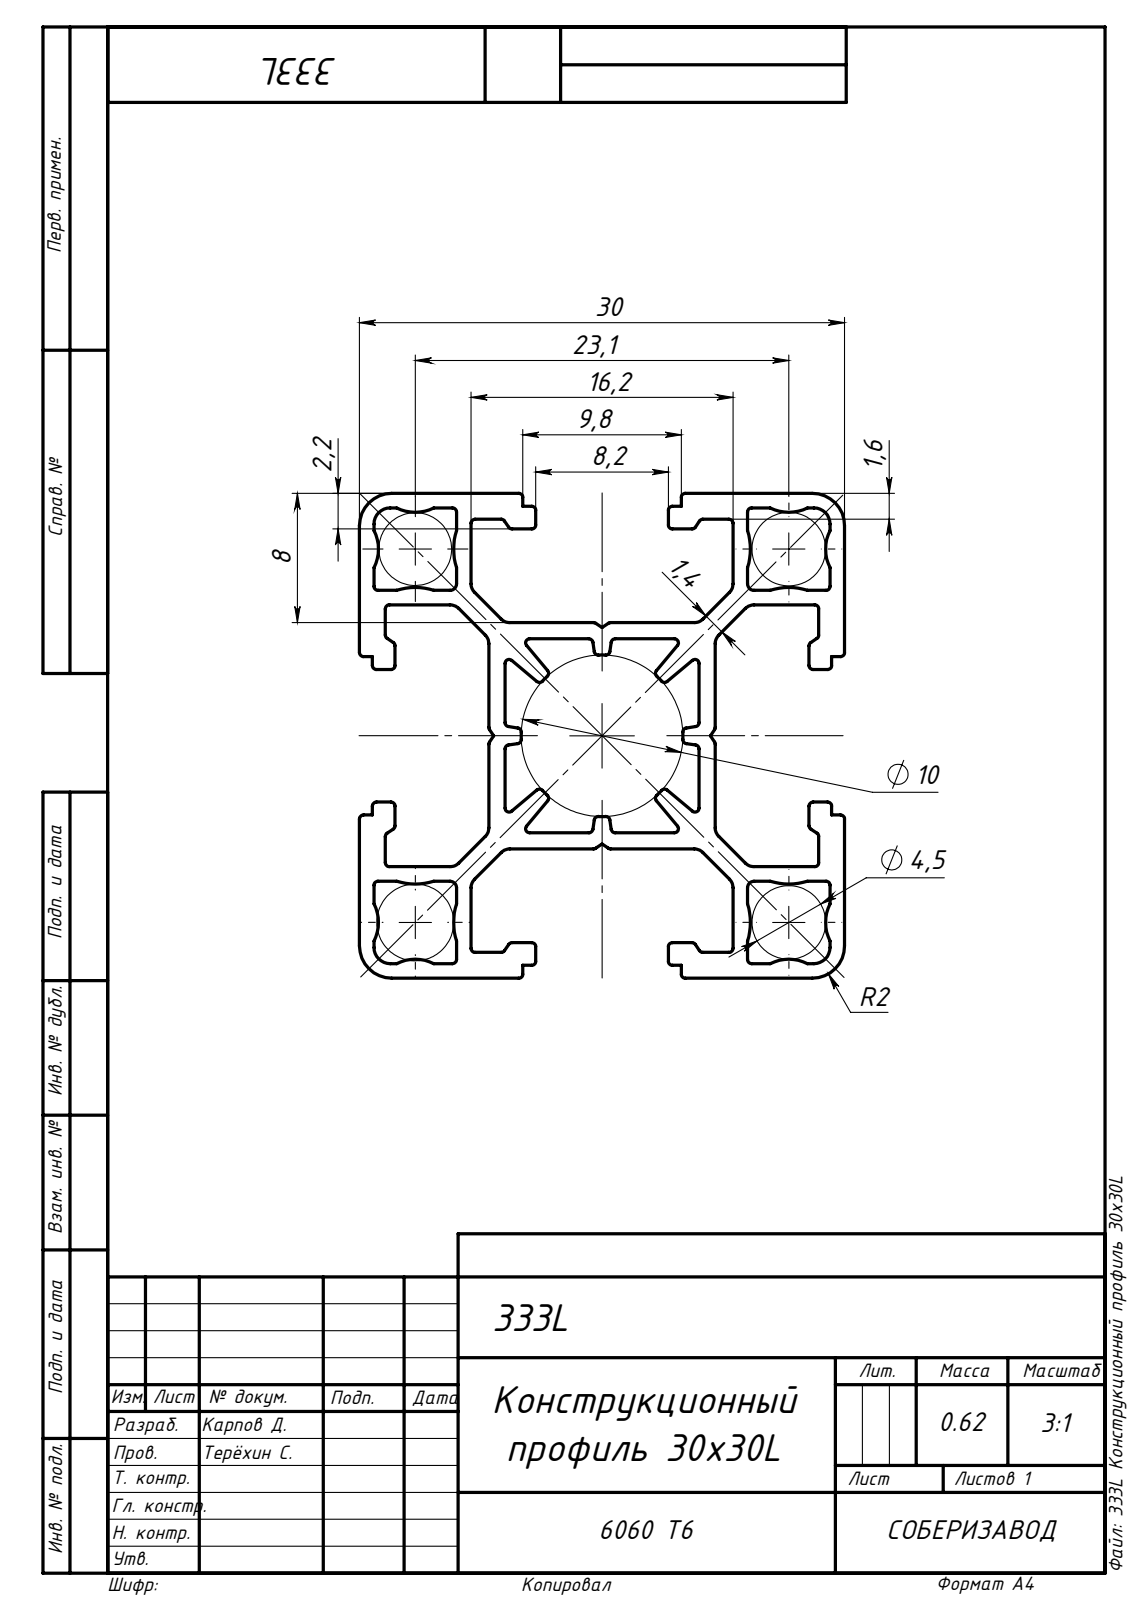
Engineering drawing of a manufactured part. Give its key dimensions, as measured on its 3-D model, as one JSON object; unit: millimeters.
{"step_written_by": "SolidWorks 2018 (AUTOMOTIVE_DESIGN)", "units": "millimeters", "bodies": {"solids": 1, "faces": 310, "planar": 146, "cylindrical": 164, "other": 0}, "overall_size": [1000, 30, 30], "volume_mm3": 227869, "surface_area_mm2": 385419, "partial_cylinders_radius": [[0.25, 96], [0.75, 16], [2.54, 8], [3.87, 8], [0.4, 4], [1, 4], [2, 4], [5, 1]], "face_to_face_distances": [23.1, 8, 22, 30, 6.9, 1.1, 15.1, 0.9, 6, 9]}
